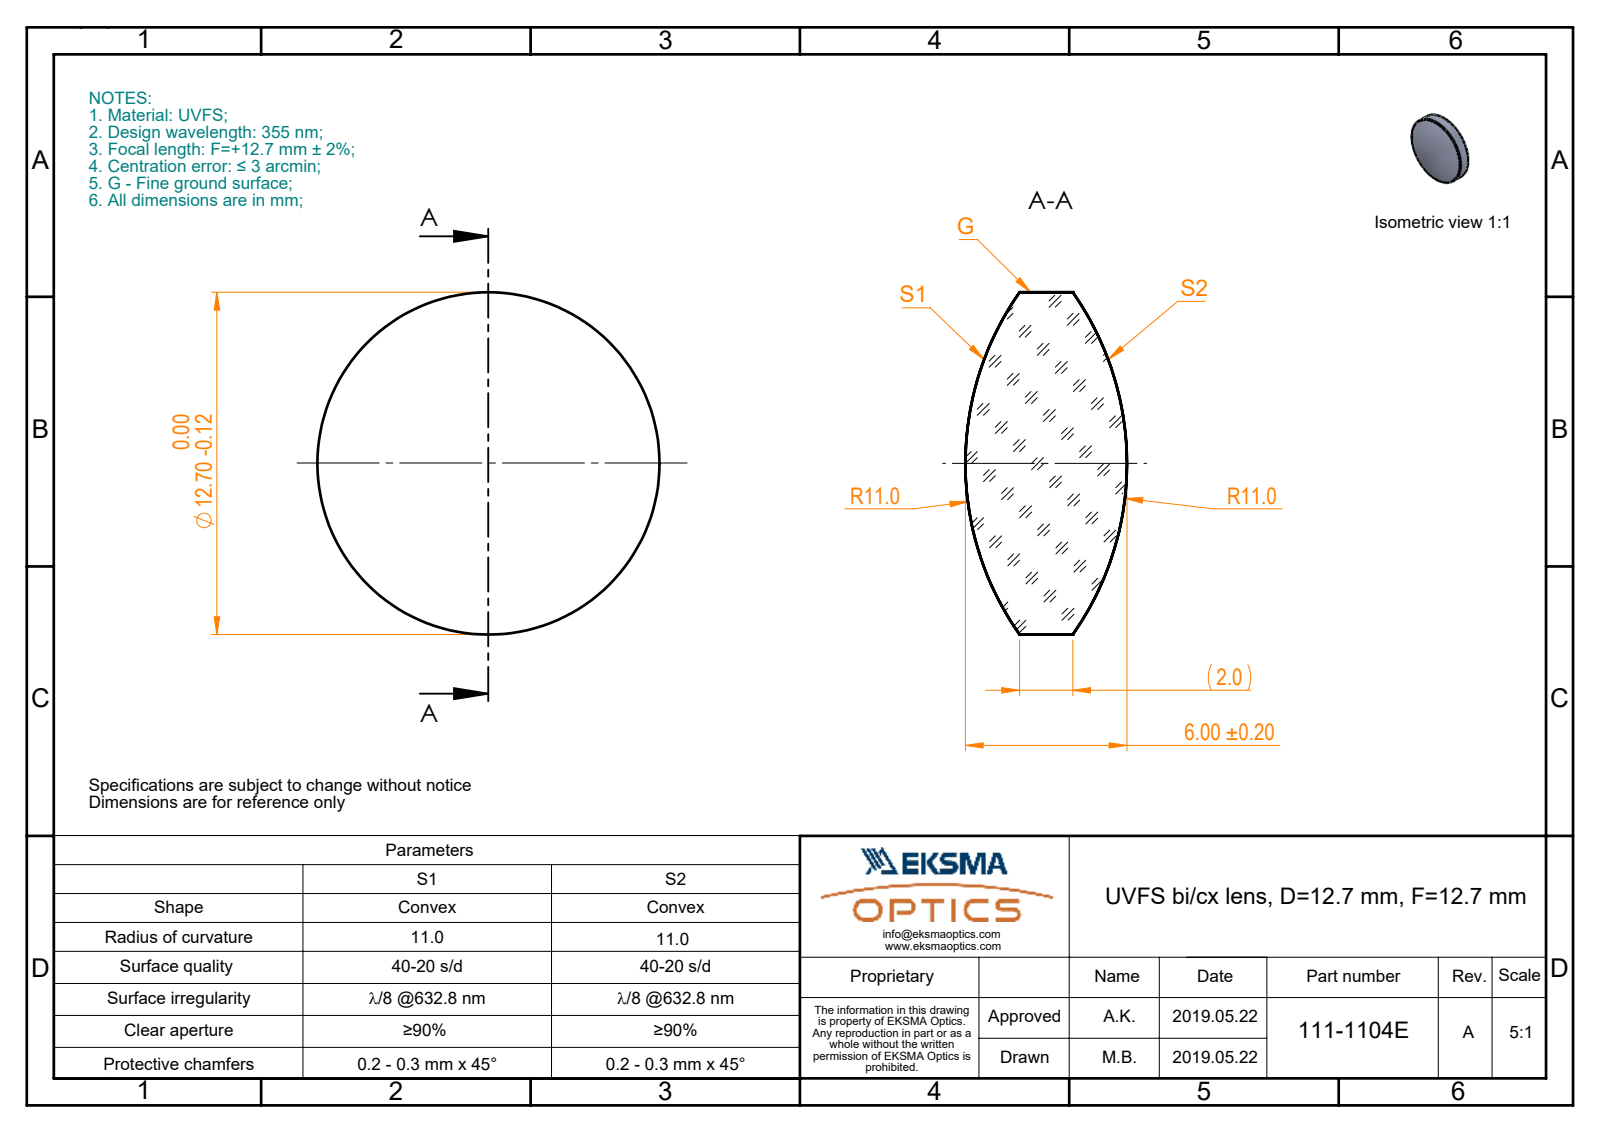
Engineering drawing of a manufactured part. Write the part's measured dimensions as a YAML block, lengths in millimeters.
part_name: "111-1104E UVFS bi-cx 12.7 F12.7"
step_written_by: "SolidWorks 2017 (CONFIG_CONTROL_DESIGN)"
units: millimeters
bodies: {solids: 1, faces: 6, planar: 0, cylindrical: 2, other: 4}
overall_size: [12.7, 12.7, 6]
volume: 514
surface_area: 358
round_bosses_or_shafts:
  - {diameter: 12.7, count: 1}
